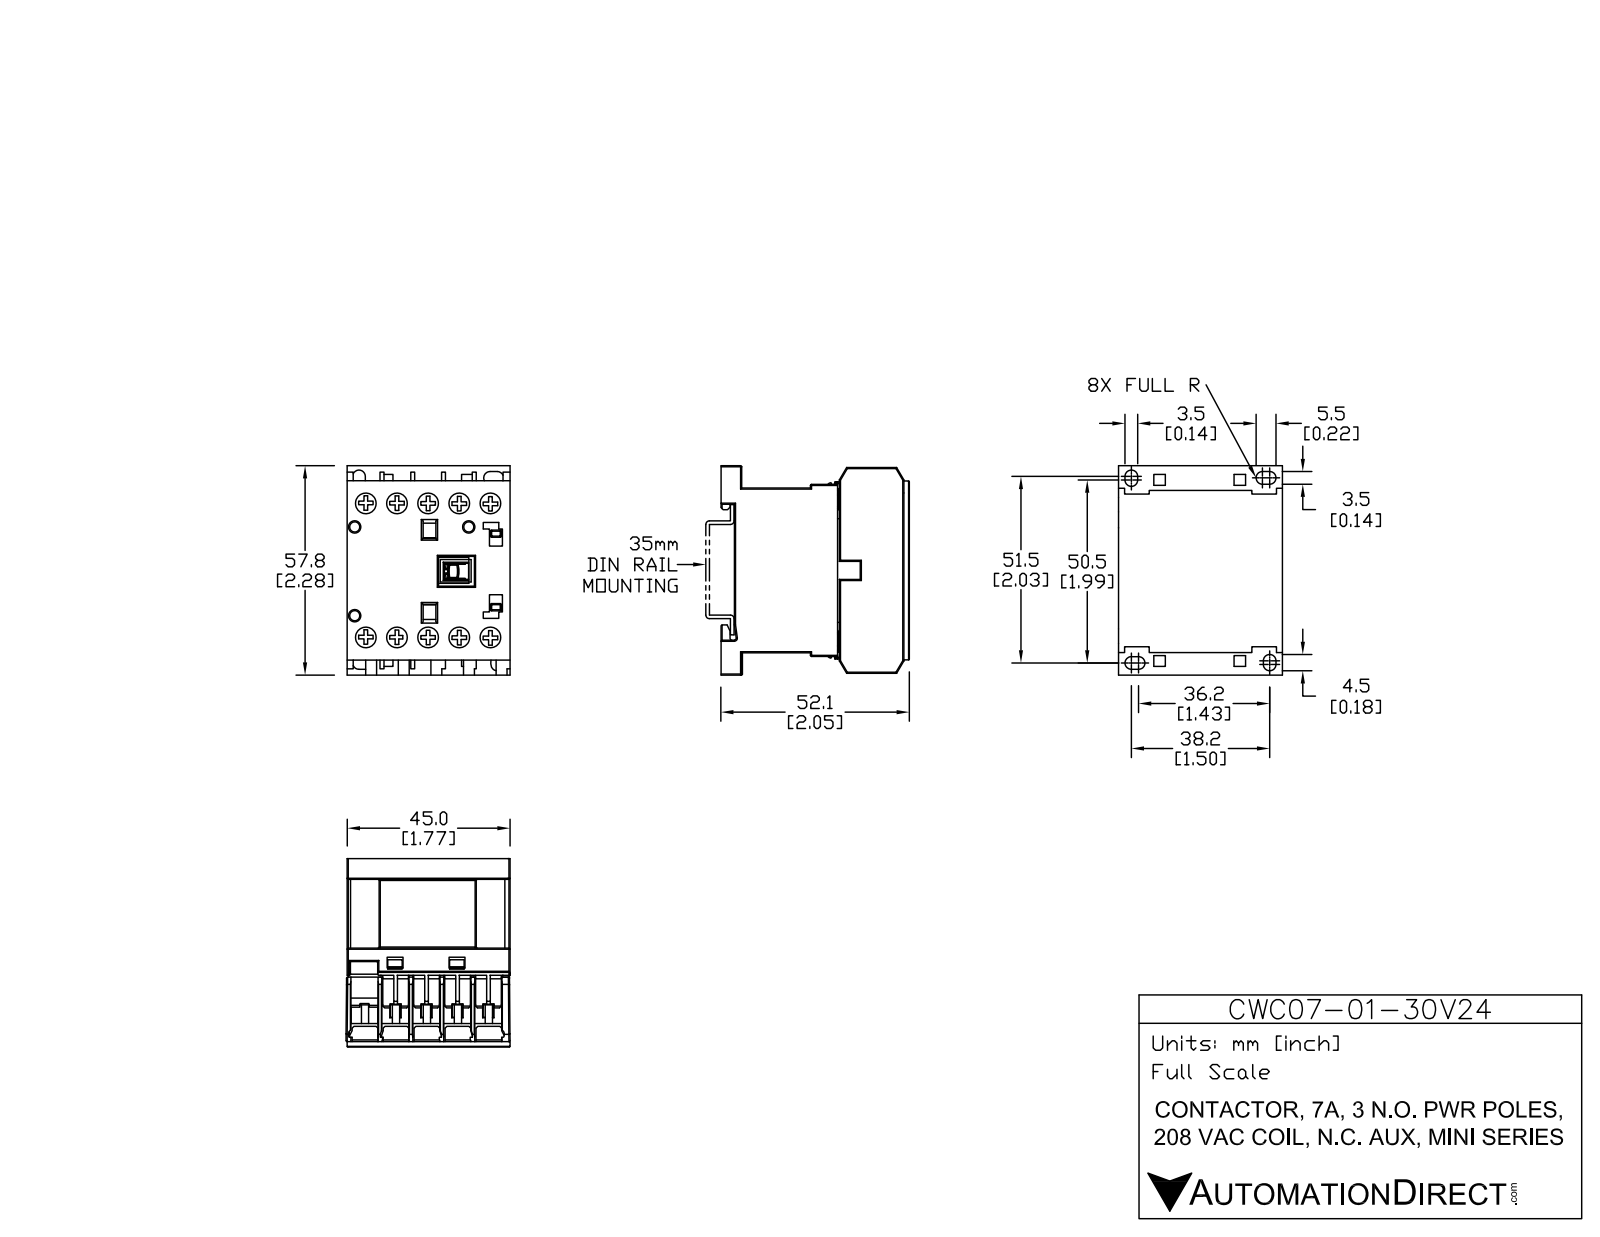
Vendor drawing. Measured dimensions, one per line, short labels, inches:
name: CWC07-01-30V24
written by: SolidWorks 2013 (AUTOMOTIVE_DESIGN)
unit: in
bodies: 15 solids, 535 faces (445 planar, 90 cylindrical, 0 other)
size: 2.285 × 2.052 × 1.801
volume: 5.927 in³; area: 47.18 in²
holes: 10× ⌀0.244, 3× ⌀0.11
bosses: 10× ⌀0.232
rounds: 20× R0.012, 6× R0.068, 2× R0.068, 1× R0.013, 1× R0.017, 1× R0.022
face distances: 0.325, 1.791, 0.049, 0.65, 0.374, 0.217, 0.699, 0.202, 0.419, 0.276
hole spacings: 0.337, 1.494, 0.673, 1.603, 1.455, 1.01, 1.771, 0.272
